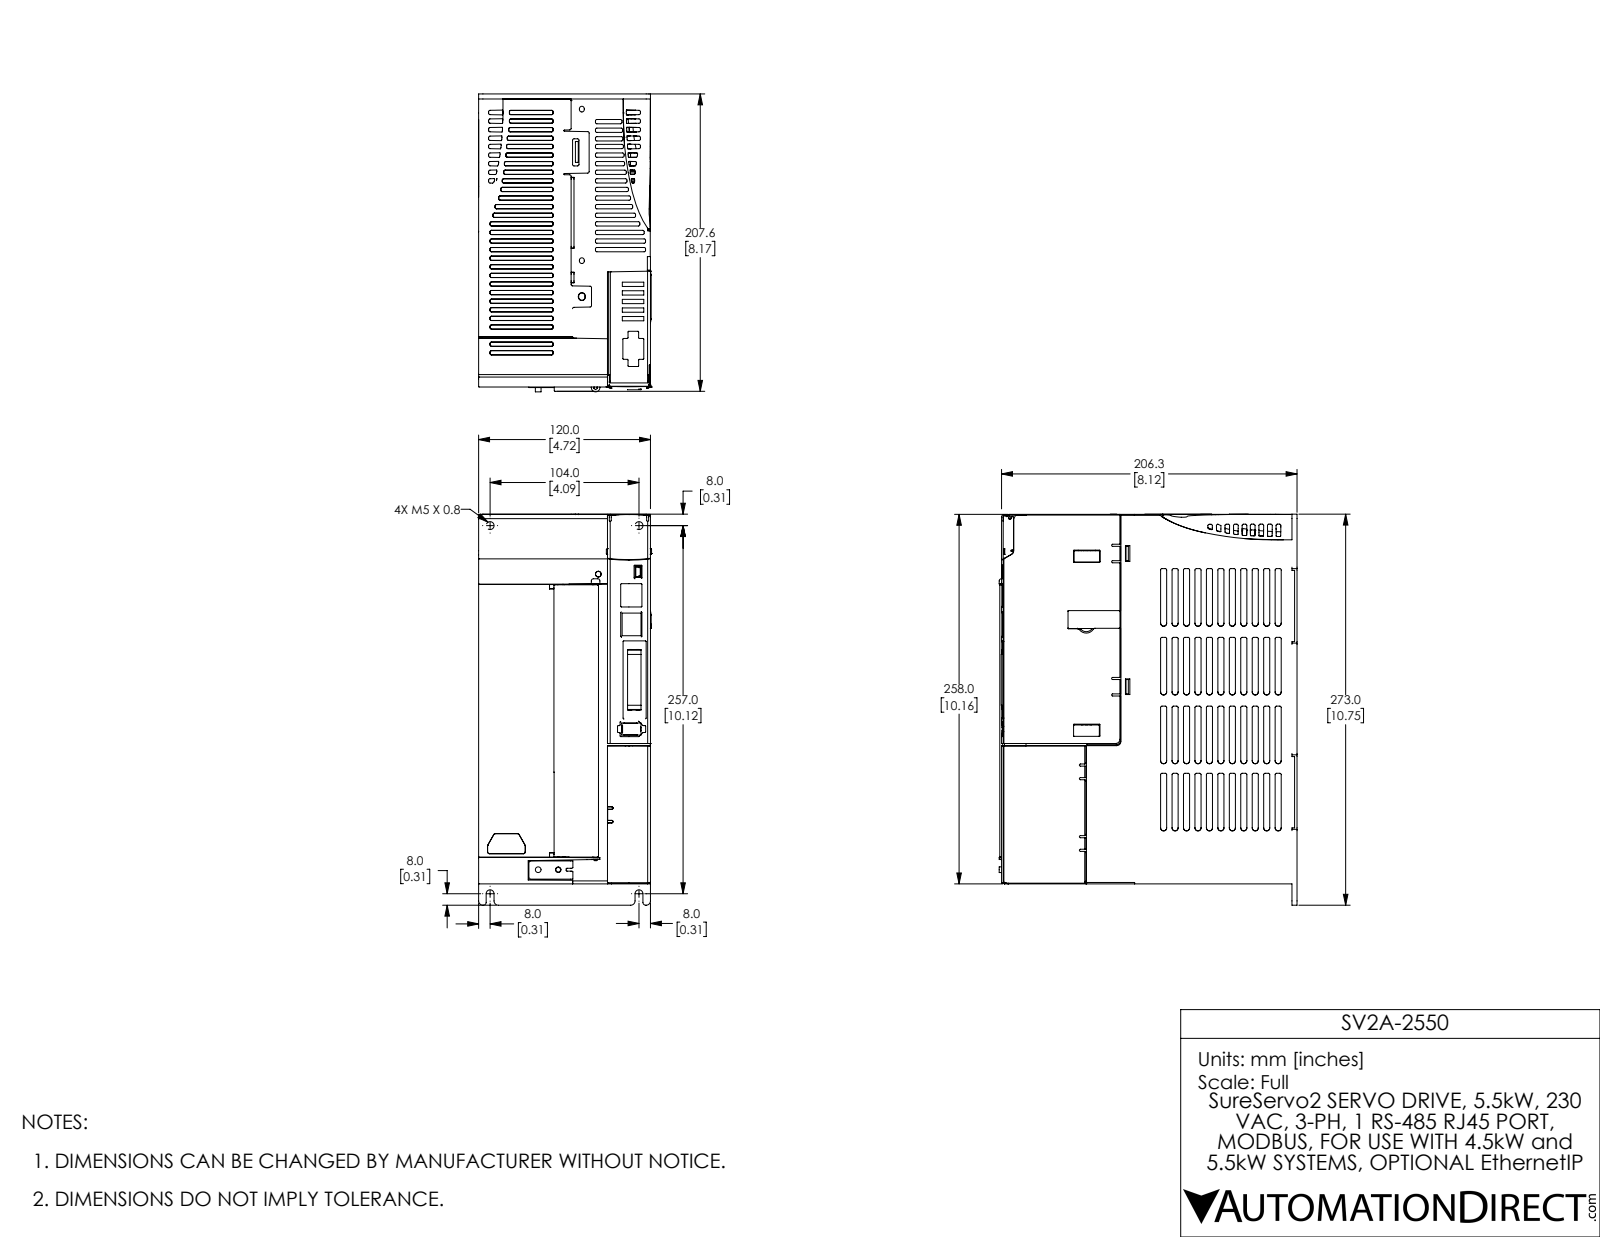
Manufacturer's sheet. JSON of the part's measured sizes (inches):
{"part_name": "SV2A-4550-20200930 redc 1 Ext 2Db Coord 2C red1 ext C2b NEW EXTs LOFT Try1De red1c r1b", "step_written_by": "SolidWorks 2017 (AUTOMOTIVE_DESIGN)", "units": "inches", "bodies": {"solids": 9, "faces": 3704, "planar": 1872, "cylindrical": 914, "other": 918}, "overall_size": [10.748, 8.189, 4.756], "volume_in3": 372.5, "surface_area_in2": 514.6, "round_holes": [[0.13, 2], [0.217, 2]], "round_bosses_or_shafts": [[0.13, 2], [0.118, 2], [0.157, 1], [0.02, 1]], "partial_cylinders_radius": [[0.039, 316], [0.02, 118], [0.012, 96], [0.084, 44], [0.004, 21], [0.008, 18], [0.079, 17], [0.01, 12]], "face_to_face_distances": [4.724, 0.139, 4.641, 0.079, 0.144, 4.719, 10.157, 0.084, 4.646, 7.465], "hole_center_spacings": [0.551, 4.094, 9.55, 9.642, 9.715, 9.856]}
